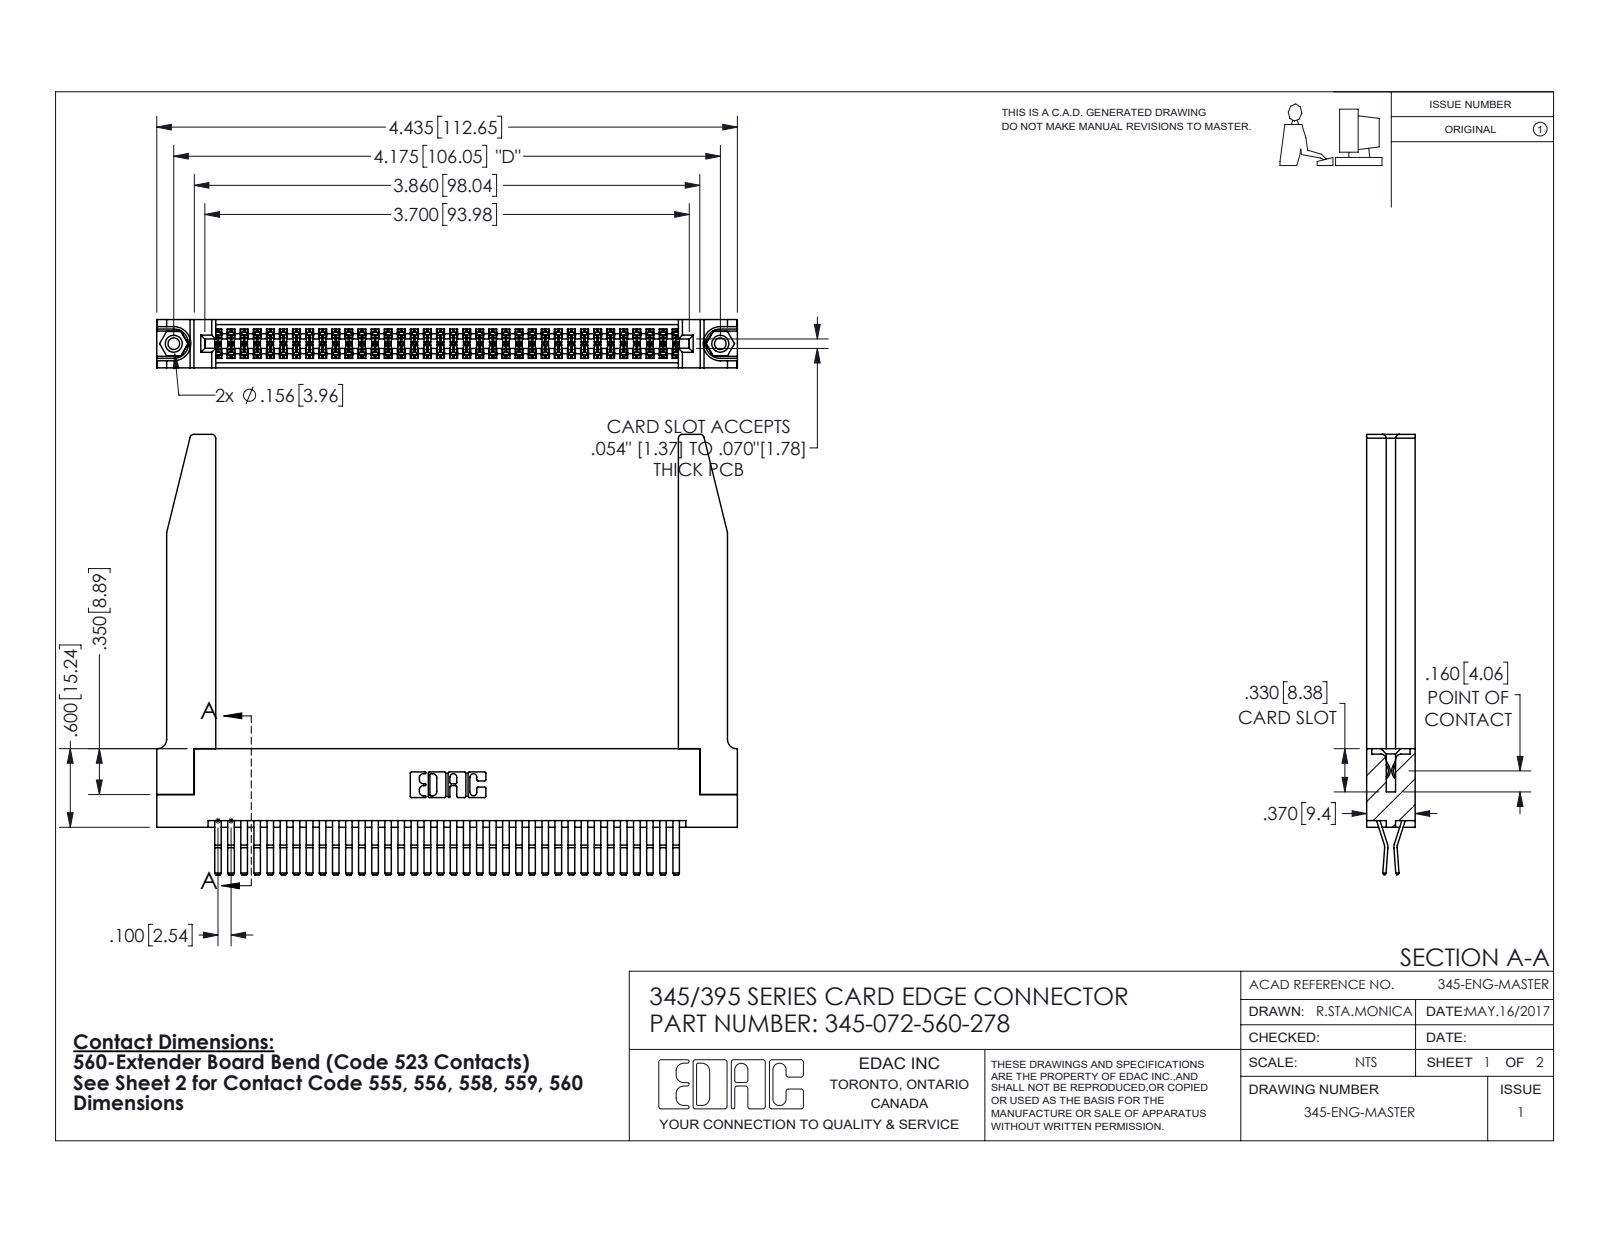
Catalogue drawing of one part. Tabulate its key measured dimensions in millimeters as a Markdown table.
| quantity | value |
| --- | --- |
| part name | 345-220-078_345-220-078; 345 Part_Flush Mounting Lugs - 0.156 Dia-TH; 345-072-560-278; 345-292-001_560 Tail (+1 more) |
| STEP written by | SolidWorks 2016 (CONFIG_CONTROL_DESIGN) |
| units | millimeters |
| bodies | 77 solids, 4104 faces (2598 planar, 1454 cylindrical, 52 other) |
| overall size | 112.7 × 85.4 × 9.4 |
| volume | 19 140 mm³ |
| surface area | 24 730 mm² |
| round holes (diameter × count) | 2.3 × 2, 3.2 × 2, 4 × 2, 1.6 × 1 |
| round bosses / shafts (diameter × count) | 3.9 × 2 |
| partial cylindrical surfaces (radius × count) | 0.2 × 108, 0.3 × 22, 0.8 × 8, 0.2 × 6, 0.8 × 6, 0.7 × 3, 0.3 × 2, 0.4 × 2 |
| main face-to-face distances | 9.4, 1.8, 7.6, 0.6, 5.1, 2.5, 6.9, 5.7, 3.8, 3.8 |
| hole center spacings | 6.9, 100.1, 106 |
